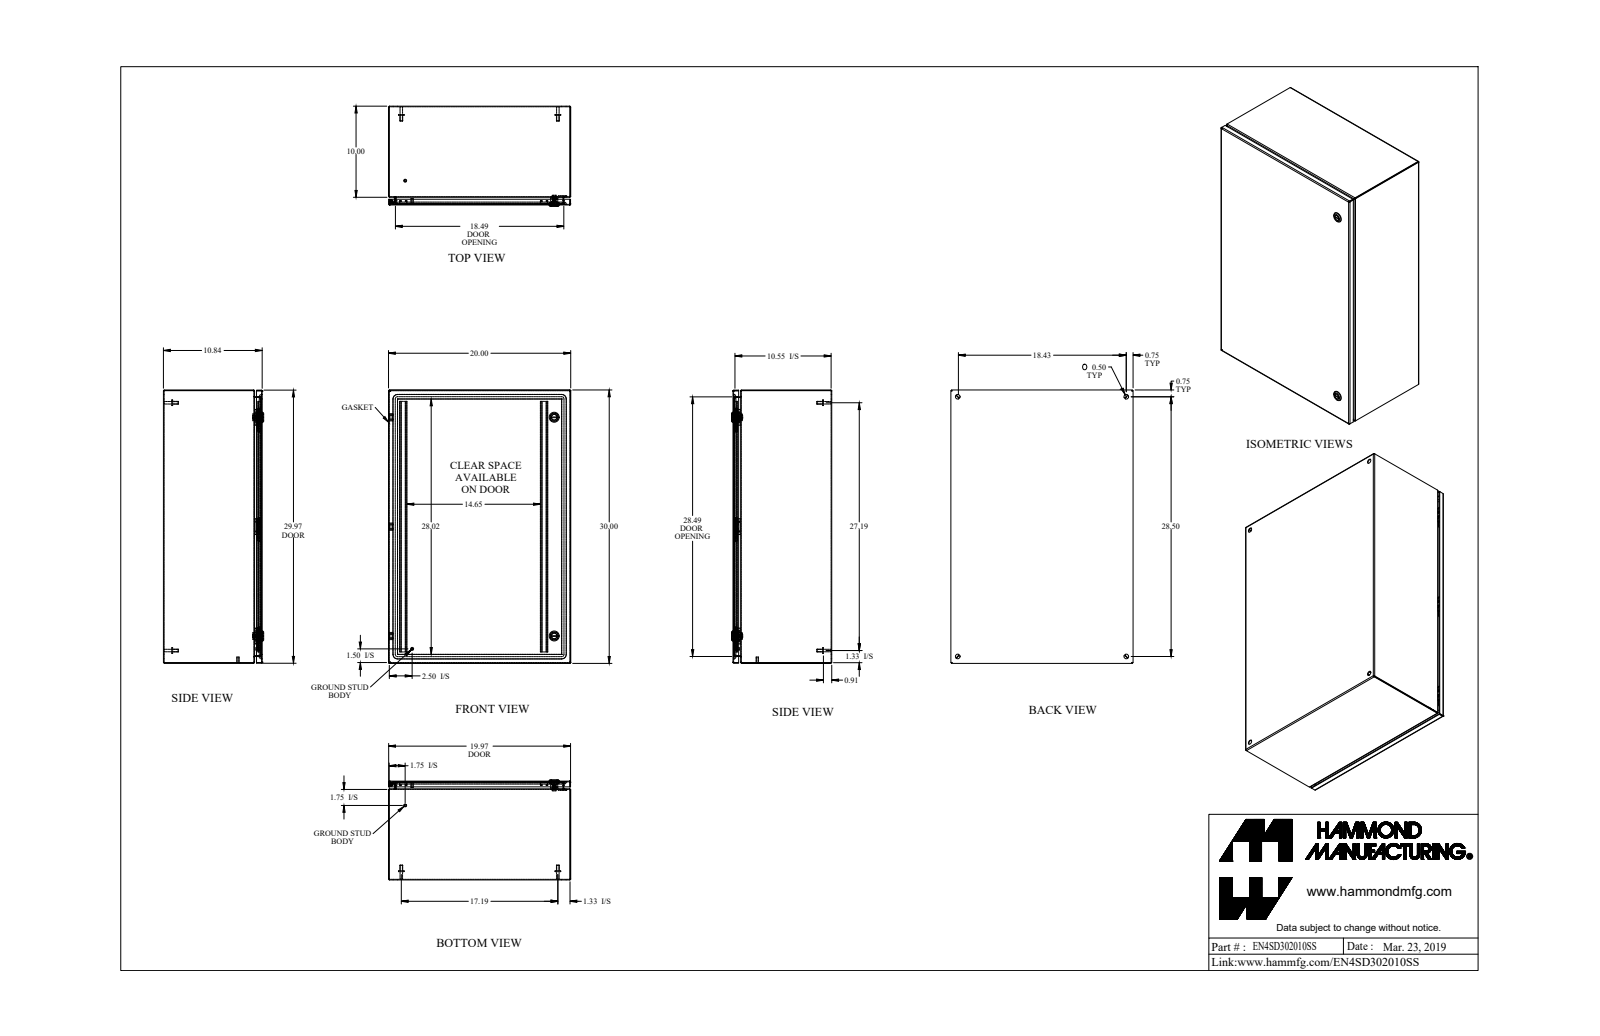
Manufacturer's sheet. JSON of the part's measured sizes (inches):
{"part_name": "EN4SD302010SS", "step_written_by": "SolidWorks 2019 (AUTOMOTIVE_DESIGN)", "units": "inches", "bodies": {"solids": 33, "faces": 892, "planar": 423, "cylindrical": 301, "other": 168}, "overall_size": [30, 20, 11.002], "volume_in3": 186.1, "surface_area_in2": 5236, "round_holes": [[0.5, 6], [0.197, 2], [0.387, 2], [0.63, 2], [0.768, 2], [0.172, 1], [0.24, 1], [0.242, 1]], "round_bosses_or_shafts": [[0.313, 6], [0.625, 4], [0.275, 4], [1.1, 2], [0.785, 2], [0.625, 2], [0.525, 2], [0.25, 2]], "partial_cylinders_radius": [[0.036, 16], [0.108, 16], [0.25, 16], [0.01, 12], [0.048, 12], [0.1, 8], [0.006, 6], [0.062, 6]], "face_to_face_distances": [0.072, 10.77, 10.698, 10.842, 19.928, 29.928, 19.856, 20, 29.856, 30], "hole_center_spacings": [2.488, 17.583, 18.5, 26.271, 28.5, 31.515, 33.978, 24]}
